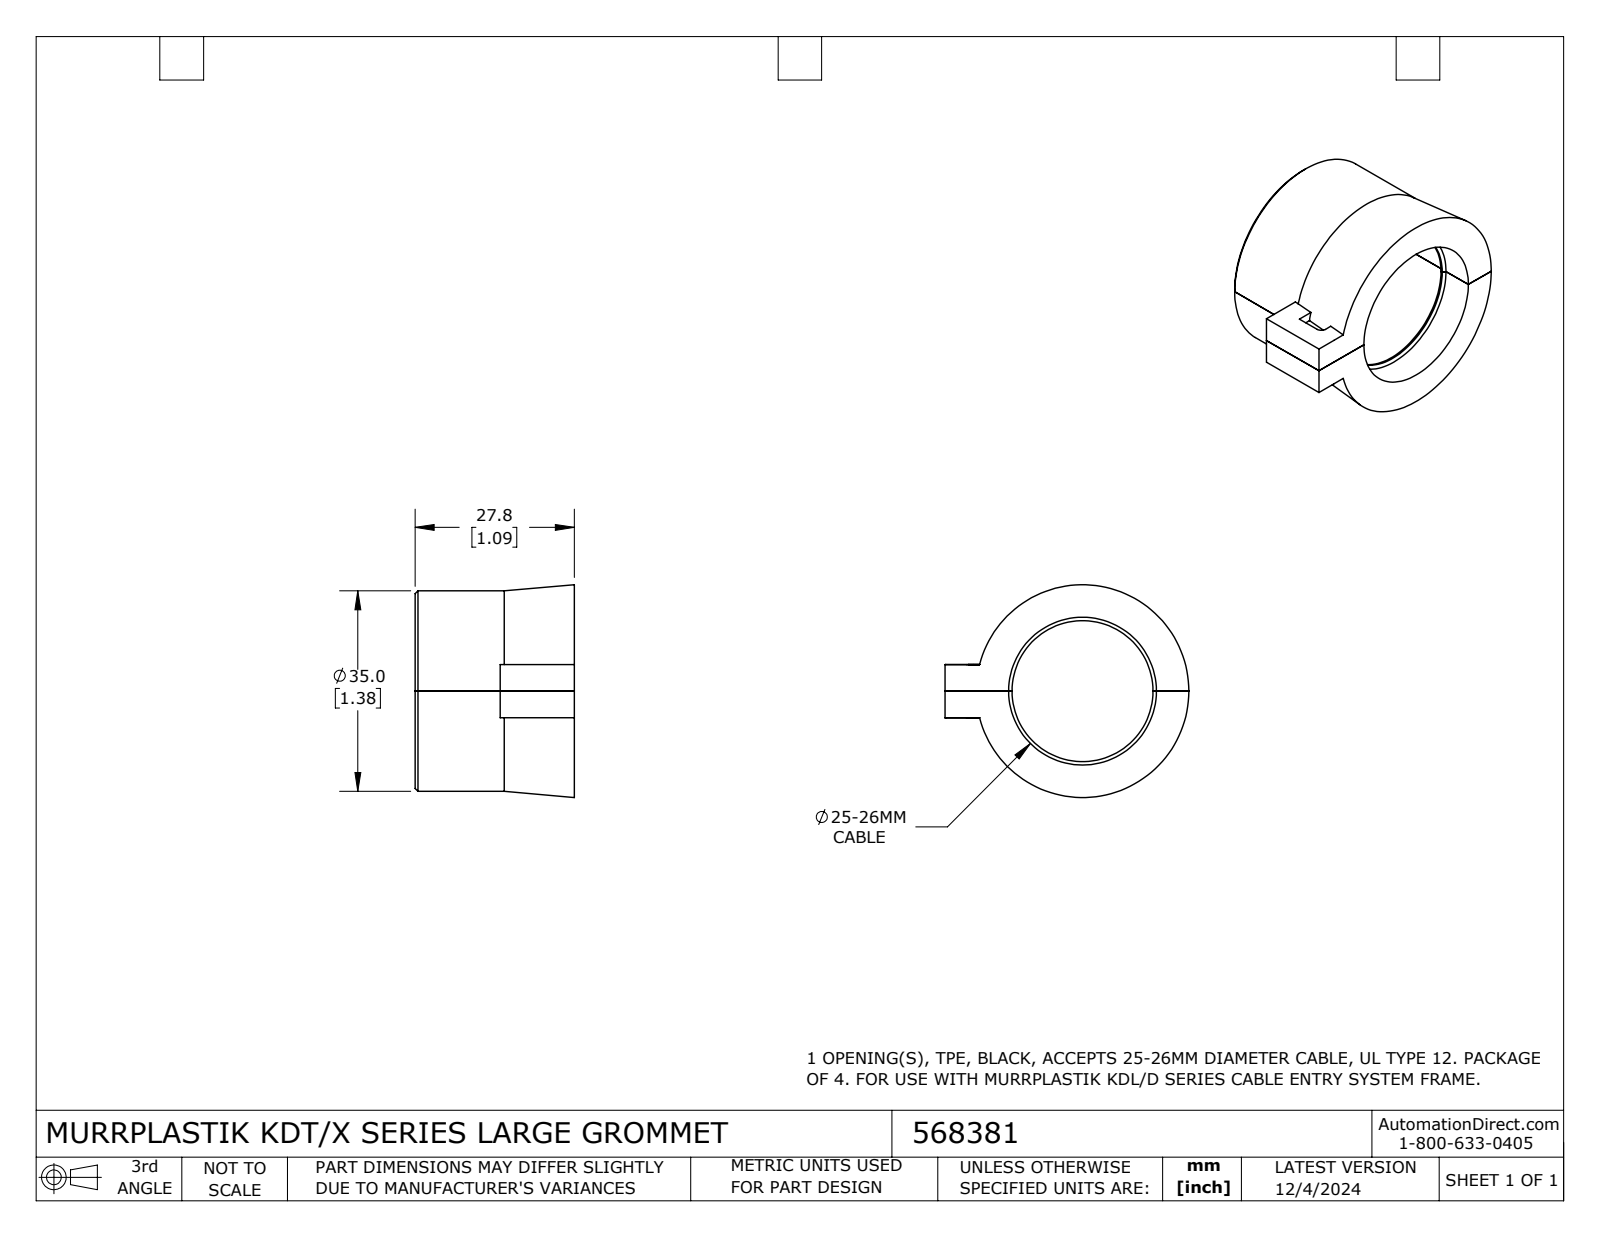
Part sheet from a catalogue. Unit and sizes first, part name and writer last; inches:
Units: inches
Overall size (bounding box): 1.676 × 1.462 × 1.094
Round holes (diameter × count): ⌀0.969 ×1, ⌀1.016 ×1
Round bosses / shafts (diameter × count): ⌀1.378 ×1
Partial cylindrical surfaces — rounded edges, fillets, slot ends (radius × count): R0.02 ×4, R0.039 ×1
Main face-to-face distances: 1.094, 0.183, 0.366, 0.51, 0.585, 0.061, 0.305, 0.122, 0.157, 0.243
Volume: 0.834 in³ · Surface area: 11.46 in²
Bodies: 2 solids, 46 faces (22 planar, 14 cylindrical, 10 other)
Part name (STEP PRODUCT): 568381
STEP written by: SolidWorks 2024 (AUTOMOTIVE_DESIGN)
